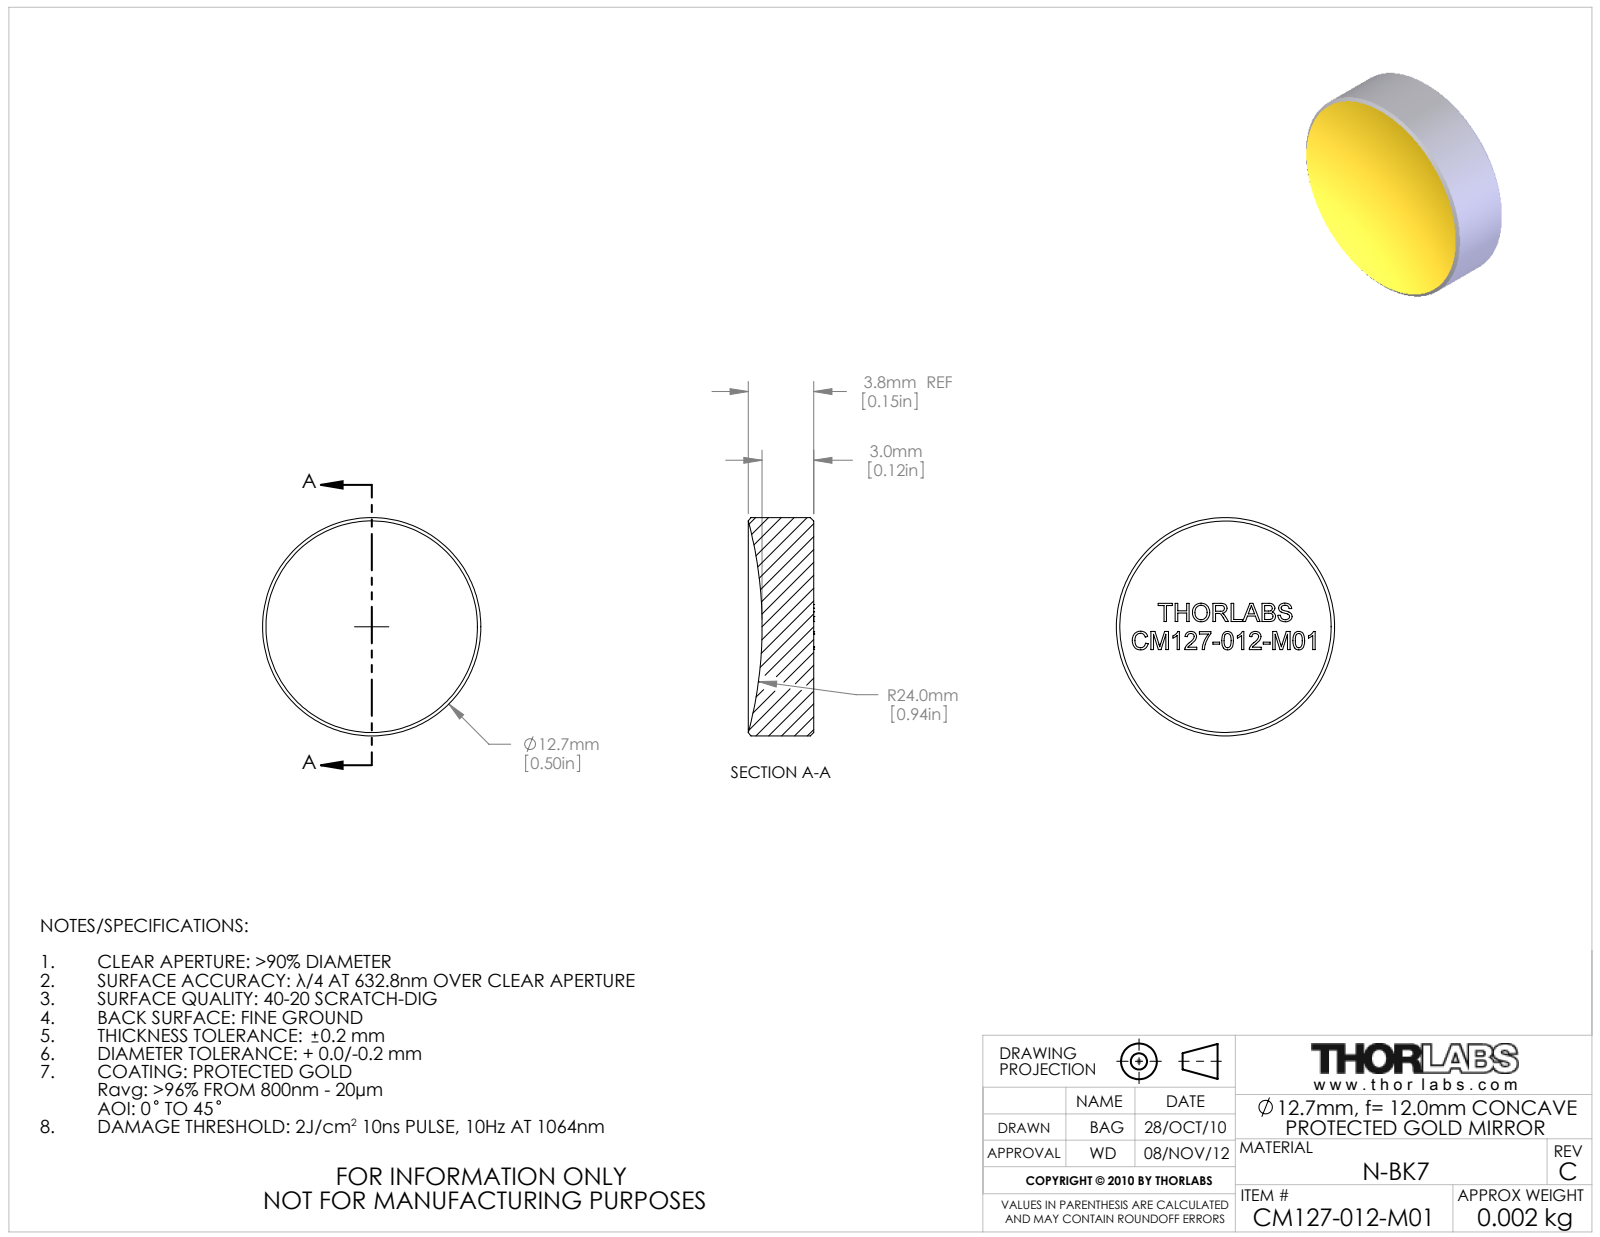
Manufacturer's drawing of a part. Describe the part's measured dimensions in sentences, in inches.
The part is named "17579-E0W". Its 3-D file was written by "SolidWorks 2009 (AUTOMOTIVE_DESIGN)". It is 1 solid with 261 faces: 152 planar, 2 cylindrical and 107 other. Overall it measures 0.5 by 0.5 by 0.15 inches. Its volume is 0.026 cubic inches and its surface area 0.618 square inches. Round bosses or shafts: 1 of diameter 0.5. The main face-to-face distances are 0.042, 0.064, 0.052, 0.048, 0.106, 0.102, 0.036, 0.071, 0.022, 0.082.
